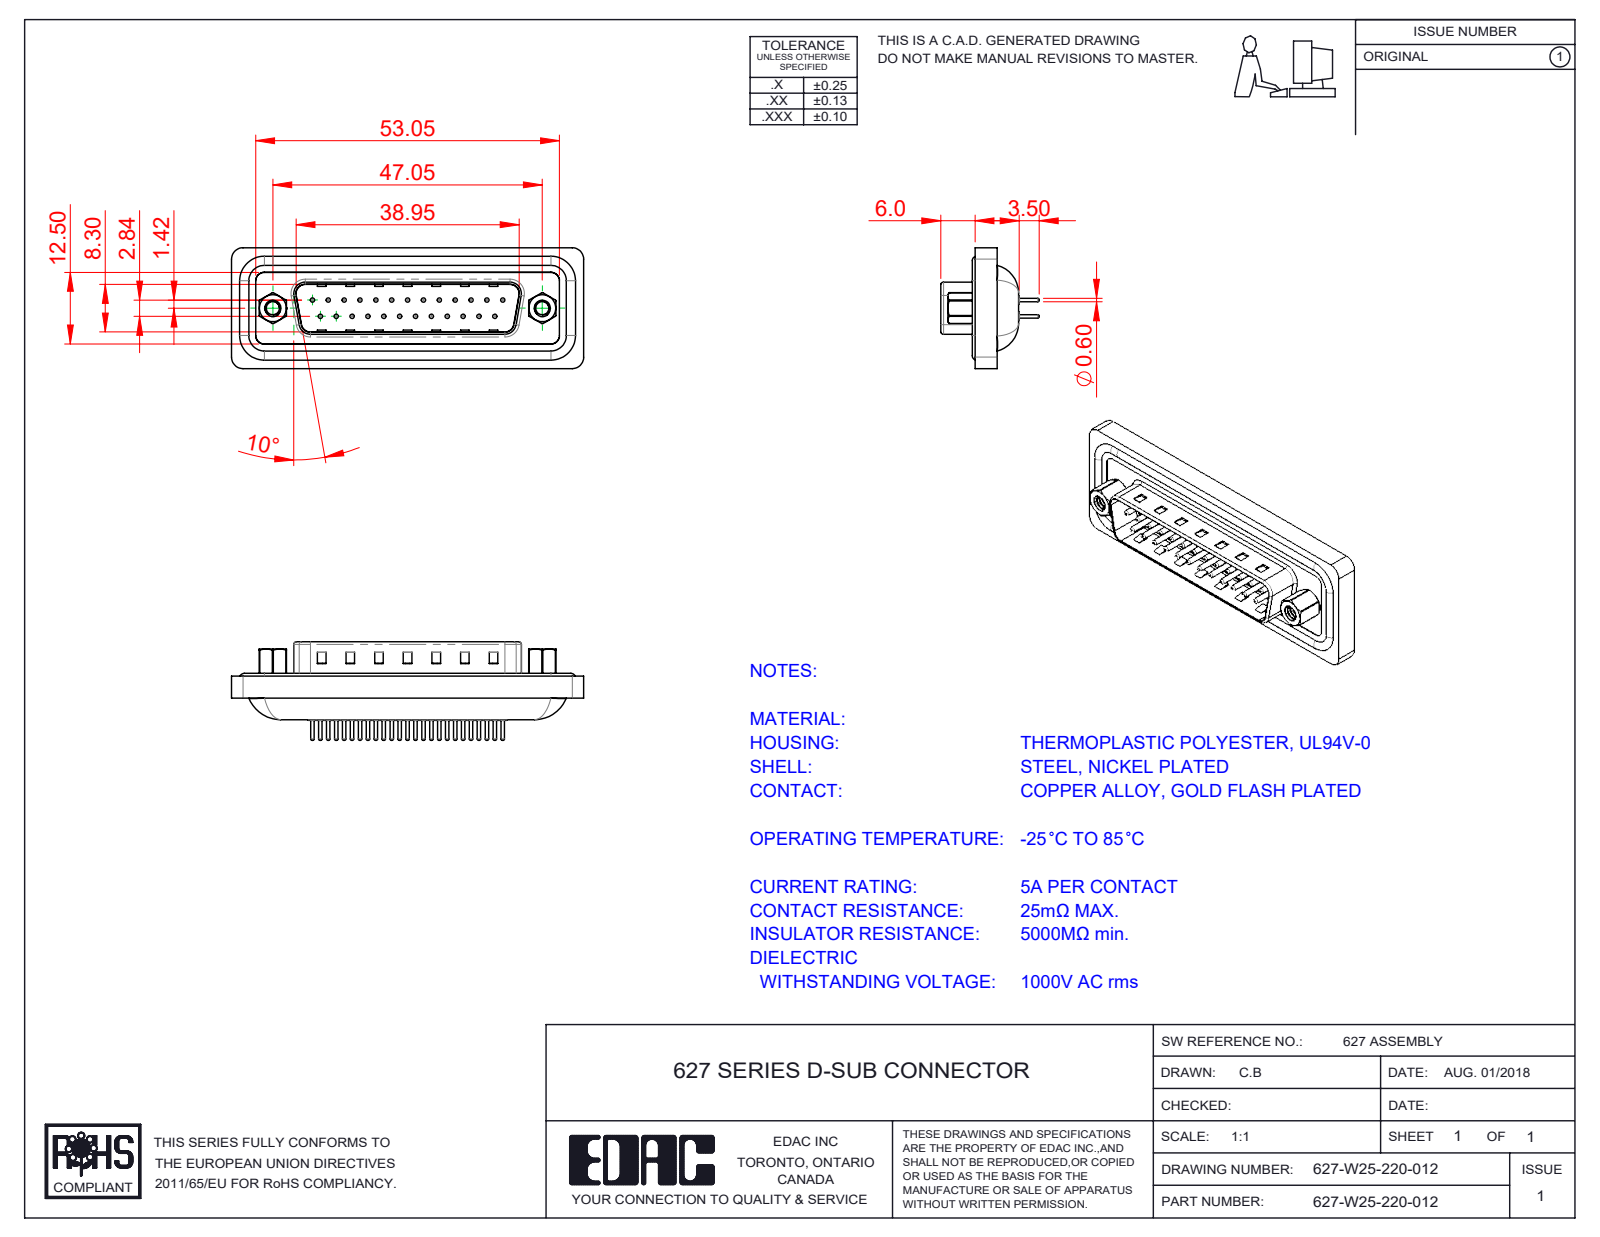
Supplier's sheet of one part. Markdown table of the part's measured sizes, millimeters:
| quantity | value |
| --- | --- |
| part name | 627W Waterproof Housing_25 Contacts; 627W 4-40 Threaded Rivet; 627W Shell Front_25 Contacts; 627W Contact Row 1_20 (+4 more) |
| STEP written by | SolidWorks 2020 (CONFIG_CONTROL_DESIGN) |
| units | millimeters |
| bodies | 33 solids, 1495 faces (380 planar, 620 cylindrical, 495 other) |
| overall size | 61.5 × 21.1 × 17.2 |
| volume | 7 471 mm³ |
| surface area | 11 062 mm² |
| round holes (diameter × count) | 0.75 × 25, 1.5 × 25, 1.6 × 25, 2 × 25, 2.26 × 2, 2.29 × 2, 4 × 2, 4.8 × 2, 5 × 2 |
| round bosses / shafts (diameter × count) | 0.6 × 25, 1.5 × 7, 1.6 × 4, 4.9 × 2, 2.79 × 2 |
| partial cylindrical surfaces (radius × count) | 2 × 16, 1.5 × 14, 0.5 × 8, 2.7 × 6, 0.9 × 4, 1.6 × 4, 4.3 × 4, 0.4 × 2 |
| main face-to-face distances | 0.75, 0.4, 1.1, 2.75, 3.75, 4.6, 4.1, 0.5, 5.65, 15.45 |
| hole center spacings | 3.16, 2.77, 5.54, 8.31, 11.08, 13.85, 5.04, 16.62 |
